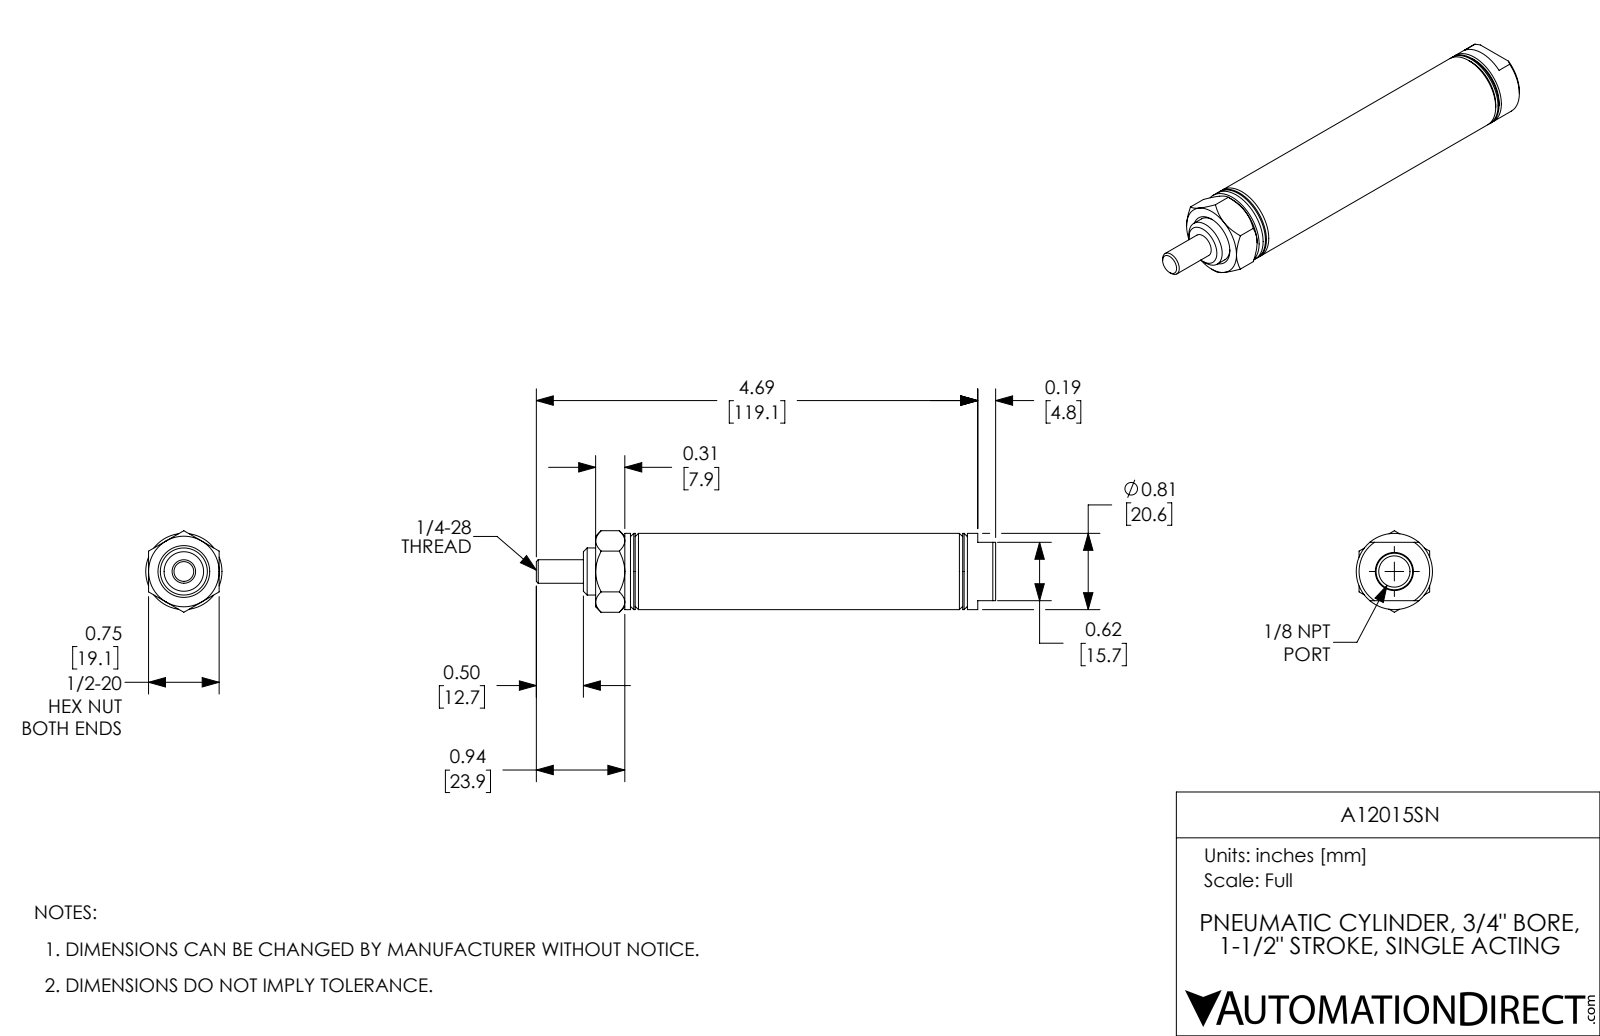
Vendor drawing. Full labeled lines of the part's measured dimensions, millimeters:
Part name (STEP PRODUCT): A12015SN; A12015SN_Mounting Nut_D-98; A12015SN-Rod; A12015SN-MainBody
STEP written by: SolidWorks 2017 (AUTOMOTIVE_DESIGN)
Units: millimetres
Bodies: 3 solids, 82 faces (25 planar, 24 cylindrical, 33 other)
Overall size (bounding box): 124 × 22 × 20.6
Volume: 24 990 mm³ · Surface area: 16 850 mm²
Round holes (diameter × count): ⌀6.4 ×1, ⌀8.4 ×1, ⌀12.7 ×1, ⌀19.1 ×1
Round bosses / shafts (diameter × count): ⌀20.6 ×1
Main face-to-face distances: 75.4, 12.7, 62.7, 50.8, 38.1, 24.6, 24.6, 37.3, 75.4, 100.1
